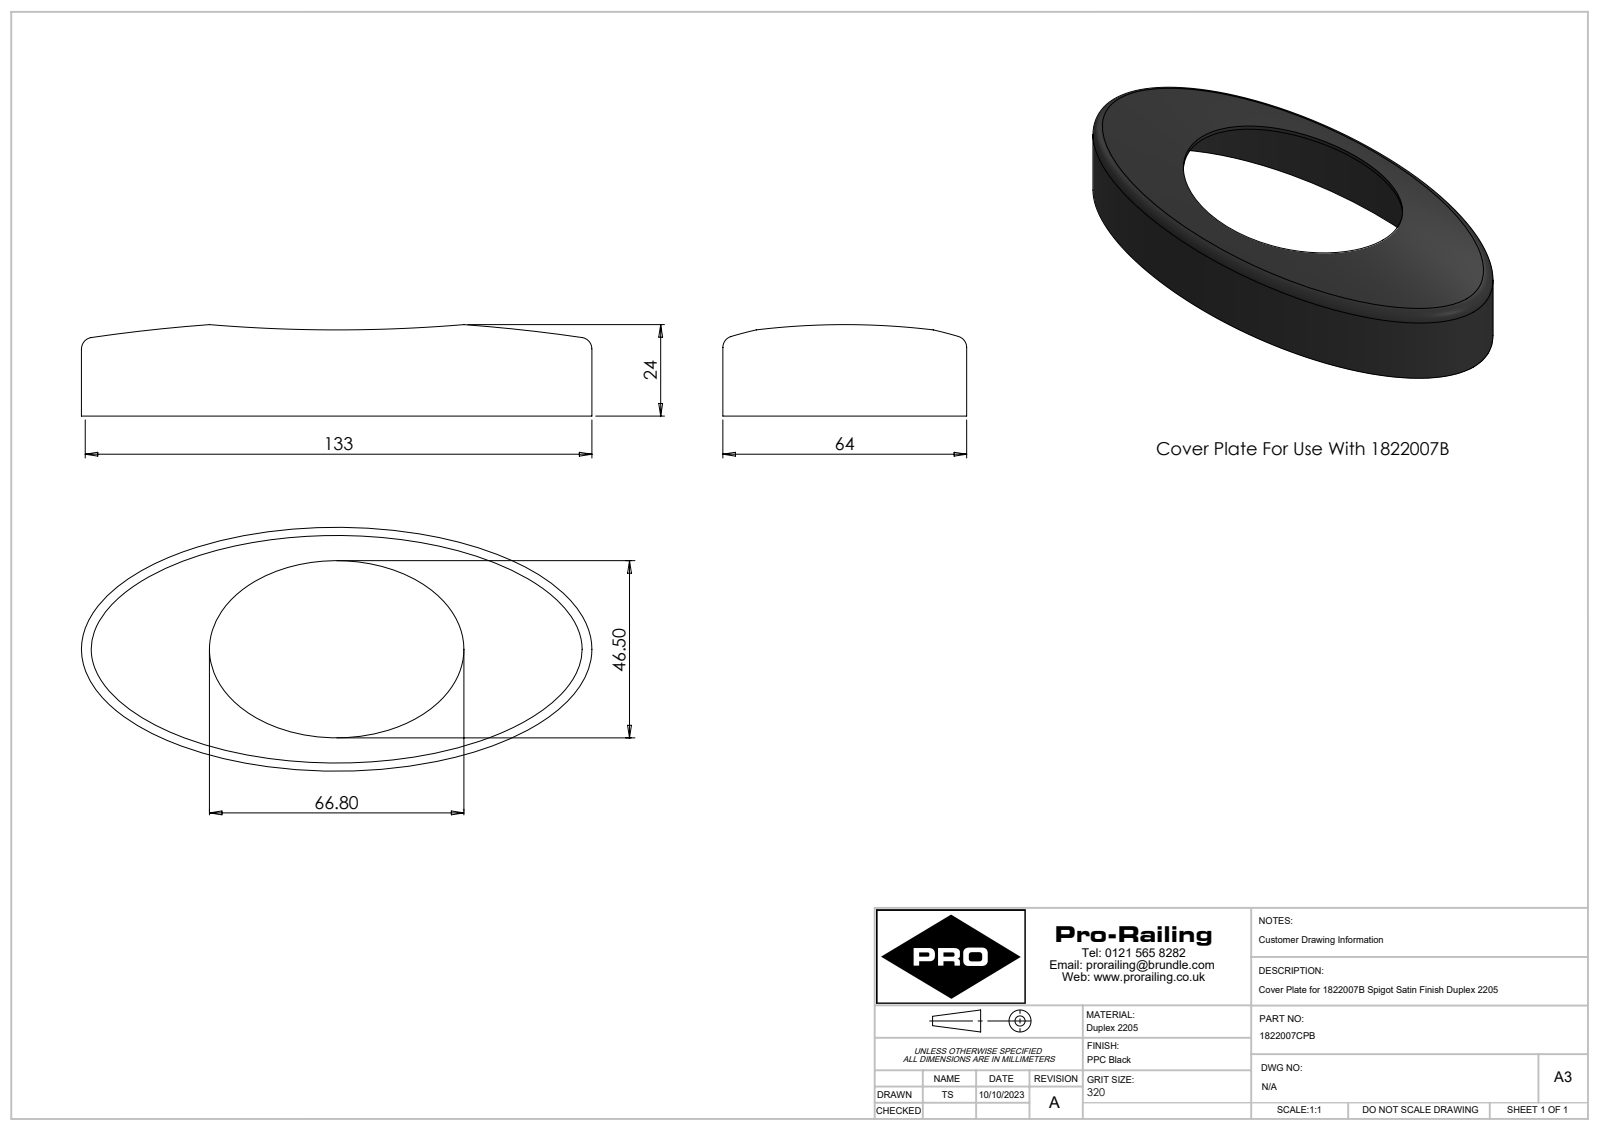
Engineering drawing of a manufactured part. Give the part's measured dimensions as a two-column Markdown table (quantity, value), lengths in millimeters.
| quantity | value |
| --- | --- |
| part name | 1822007CP |
| STEP written by | SolidWorks 2020 (CONFIG_CONTROL_DESIGN) |
| units | millimeters |
| bodies | 1 solid, 13 faces (1 planar, 0 cylindrical, 12 other) |
| overall size | 134 × 64 × 24 |
| volume | 10 318 mm³ |
| surface area | 21 149 mm² |
